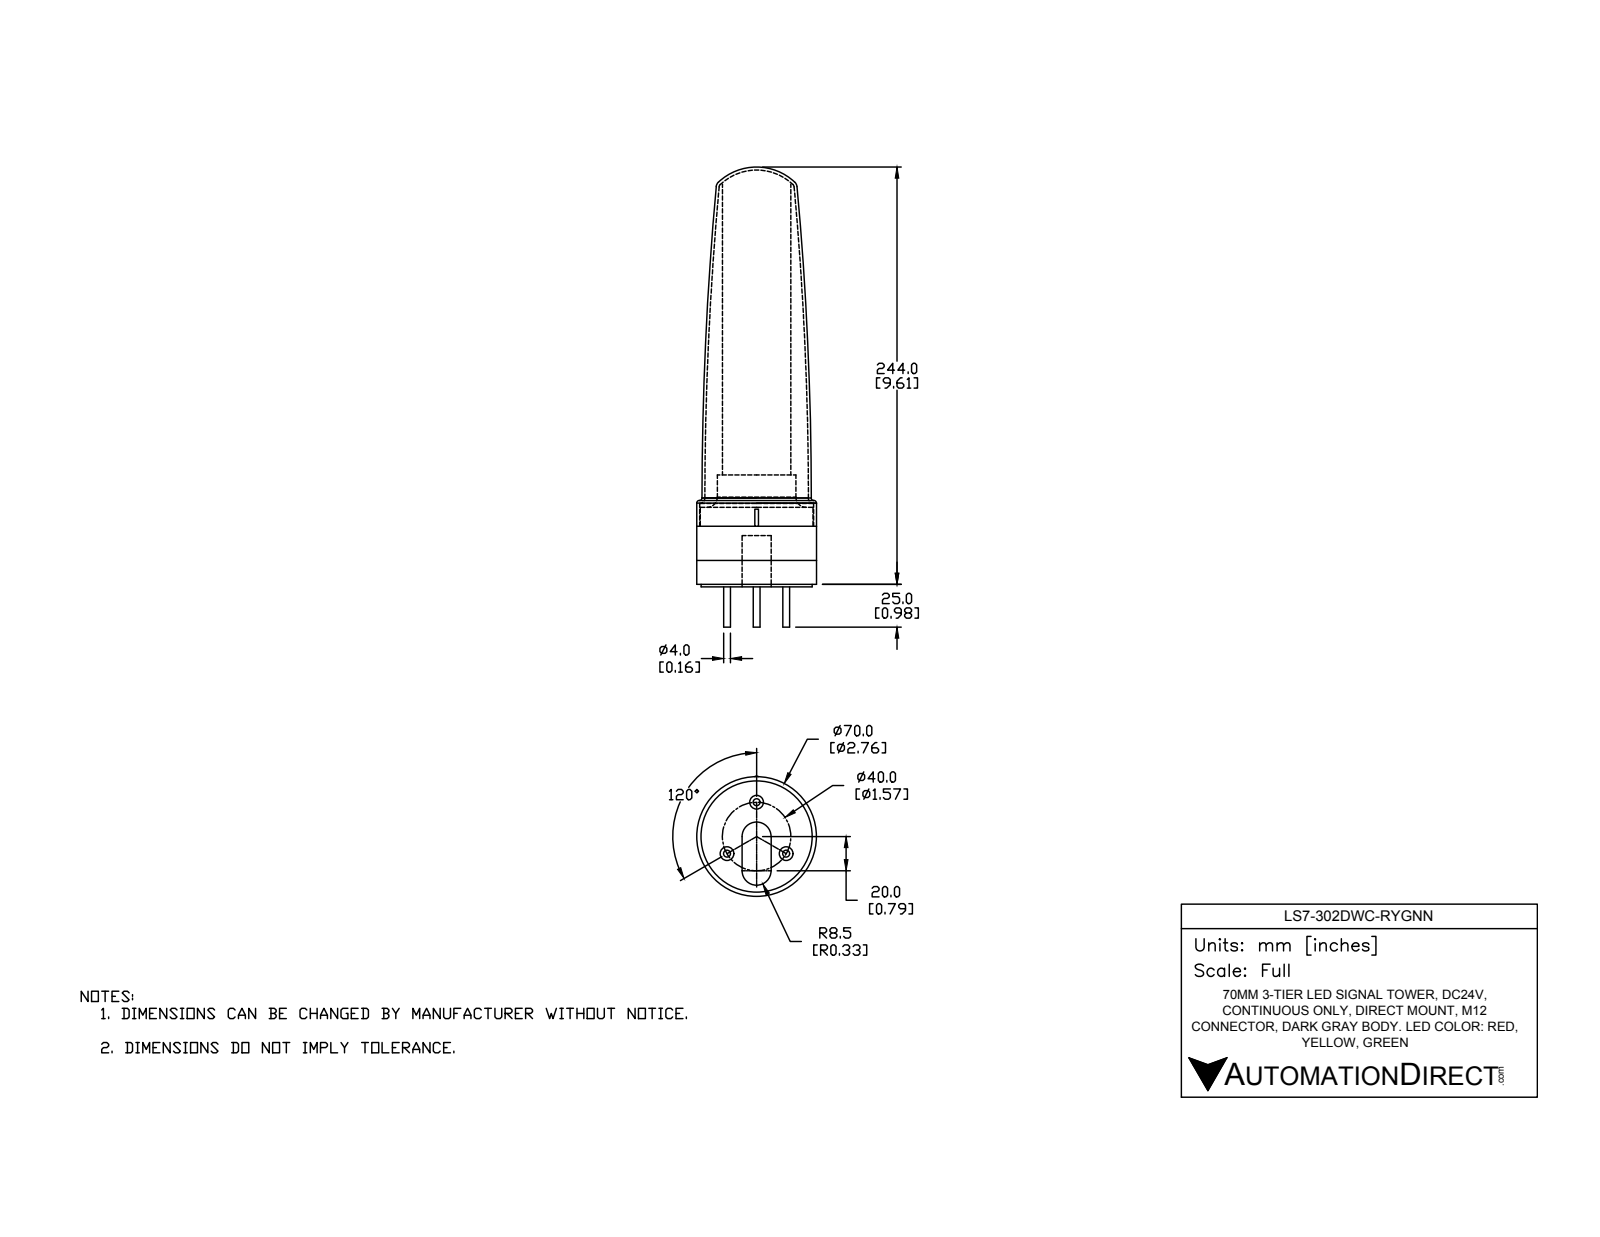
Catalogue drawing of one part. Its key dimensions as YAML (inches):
part_name: "LS7-302DWC-RYGNN"
step_written_by: "SolidWorks 2016 (AUTOMOTIVE_DESIGN)"
units: inches
bodies: {solids: 8, faces: 84, planar: 27, cylindrical: 39, other: 18}
overall_size: [10.591, 2.768, 2.756]
volume: 28.6
surface_area: 212
round_holes:
  - {diameter: 0.315, count: 3}
  - {diameter: 2.622, count: 1}
round_bosses_or_shafts:
  - {diameter: 0.157, count: 3}
  - {diameter: 2.756, count: 1}
  - {diameter: 2.598, count: 1}
  - {diameter: 2.559, count: 1}
  - {diameter: 1.811, count: 1}
  - {diameter: 1.575, count: 1}
partial_cylinders:
  - {radius: 0.335, count: 2}
  - {radius: 0.039, count: 1}
  - {radius: 0.079, count: 1}
face_to_face_distances: [0.551, 2.52, 1.969, 0.61, 0.059, 2.579, 1.181, 1.398, 9.272, 9.213]
hole_center_spacings: [0.787, 1.364]
